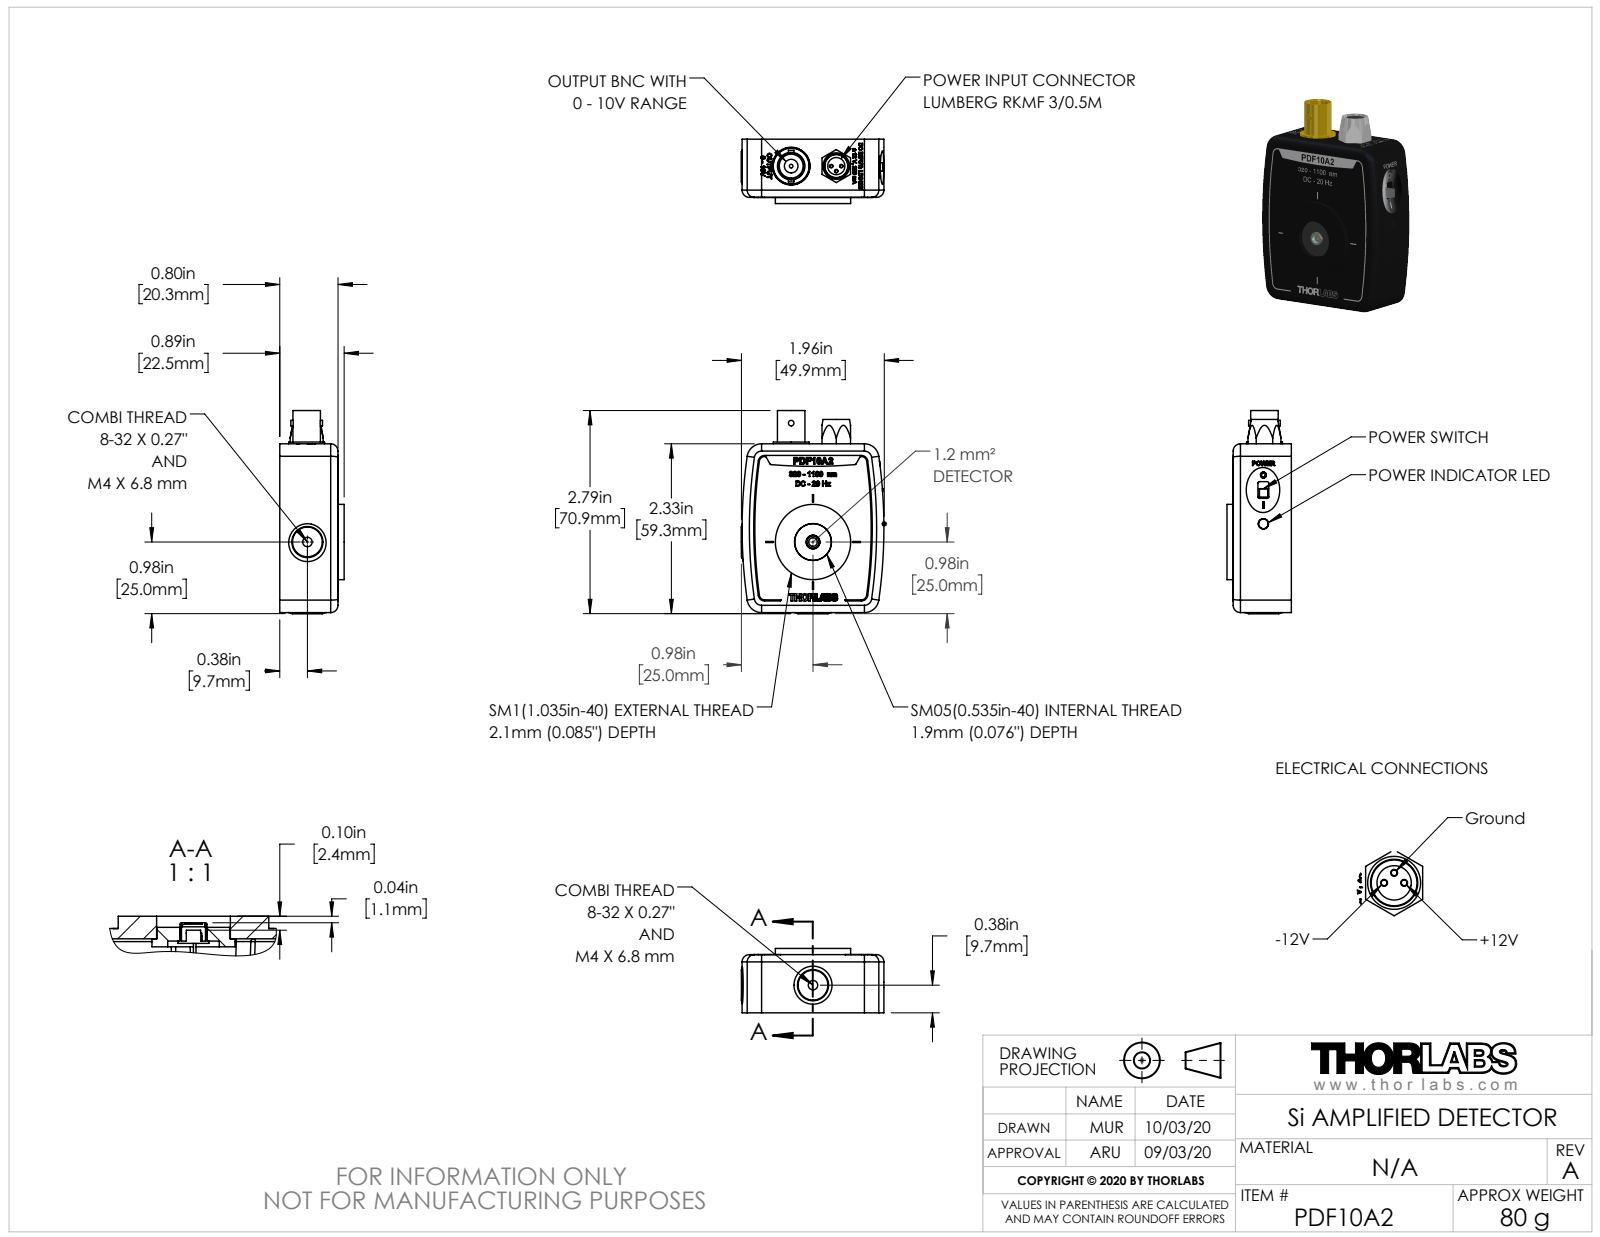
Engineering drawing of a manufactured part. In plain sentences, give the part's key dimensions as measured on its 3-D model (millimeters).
The part is named "19.04.16_PDF10A2-A". Its 3-D file was written by "SolidWorks 2018 (AUTOMOTIVE_DESIGN)". It is 0 solids with 4361 faces: 2354 planar, 311 cylindrical and 1696 other. Overall it measures 70.9 by 49.77 by 22.48 millimeters. Round holes: 7 of diameter 1.78, 5 of diameter 1, 2 of diameter 3.3, 1 of diameter 0.38, 1 of diameter 0.89, 1 of diameter 1.27, 1 of diameter 2.4, 1 of diameter 2.92, 1 of diameter 3, 1 of diameter 3.56, 1 of diameter 4.2, 1 of diameter 4.8. Round bosses or shafts: 4 of diameter 5, 4 of diameter 2.18, 3 of diameter 3.8, 3 of diameter 2, 2 of diameter 4, 2 of diameter 0.45, 1 of diameter 26.29, 1 of diameter 14.5. Partial cylindrical surfaces (rounded edges, fillets, slot ends): 18 of radius 0.51, 8 of radius 0.76, 8 of radius 2.54, 4 of radius 0.2, 4 of radius 0.56, 4 of radius 1.6, 4 of radius 1.85, 4 of radius 2.23. The main face-to-face distances are 1.5, 18.44, 16.94, 1.78, 18.72, 20.22, 58.93, 3.94, 2.16, 20.88. The hole center spacings are 1.75, 1.27, 2.47, 19.81, 28.04, 35.73, 38.1, 50.8.
